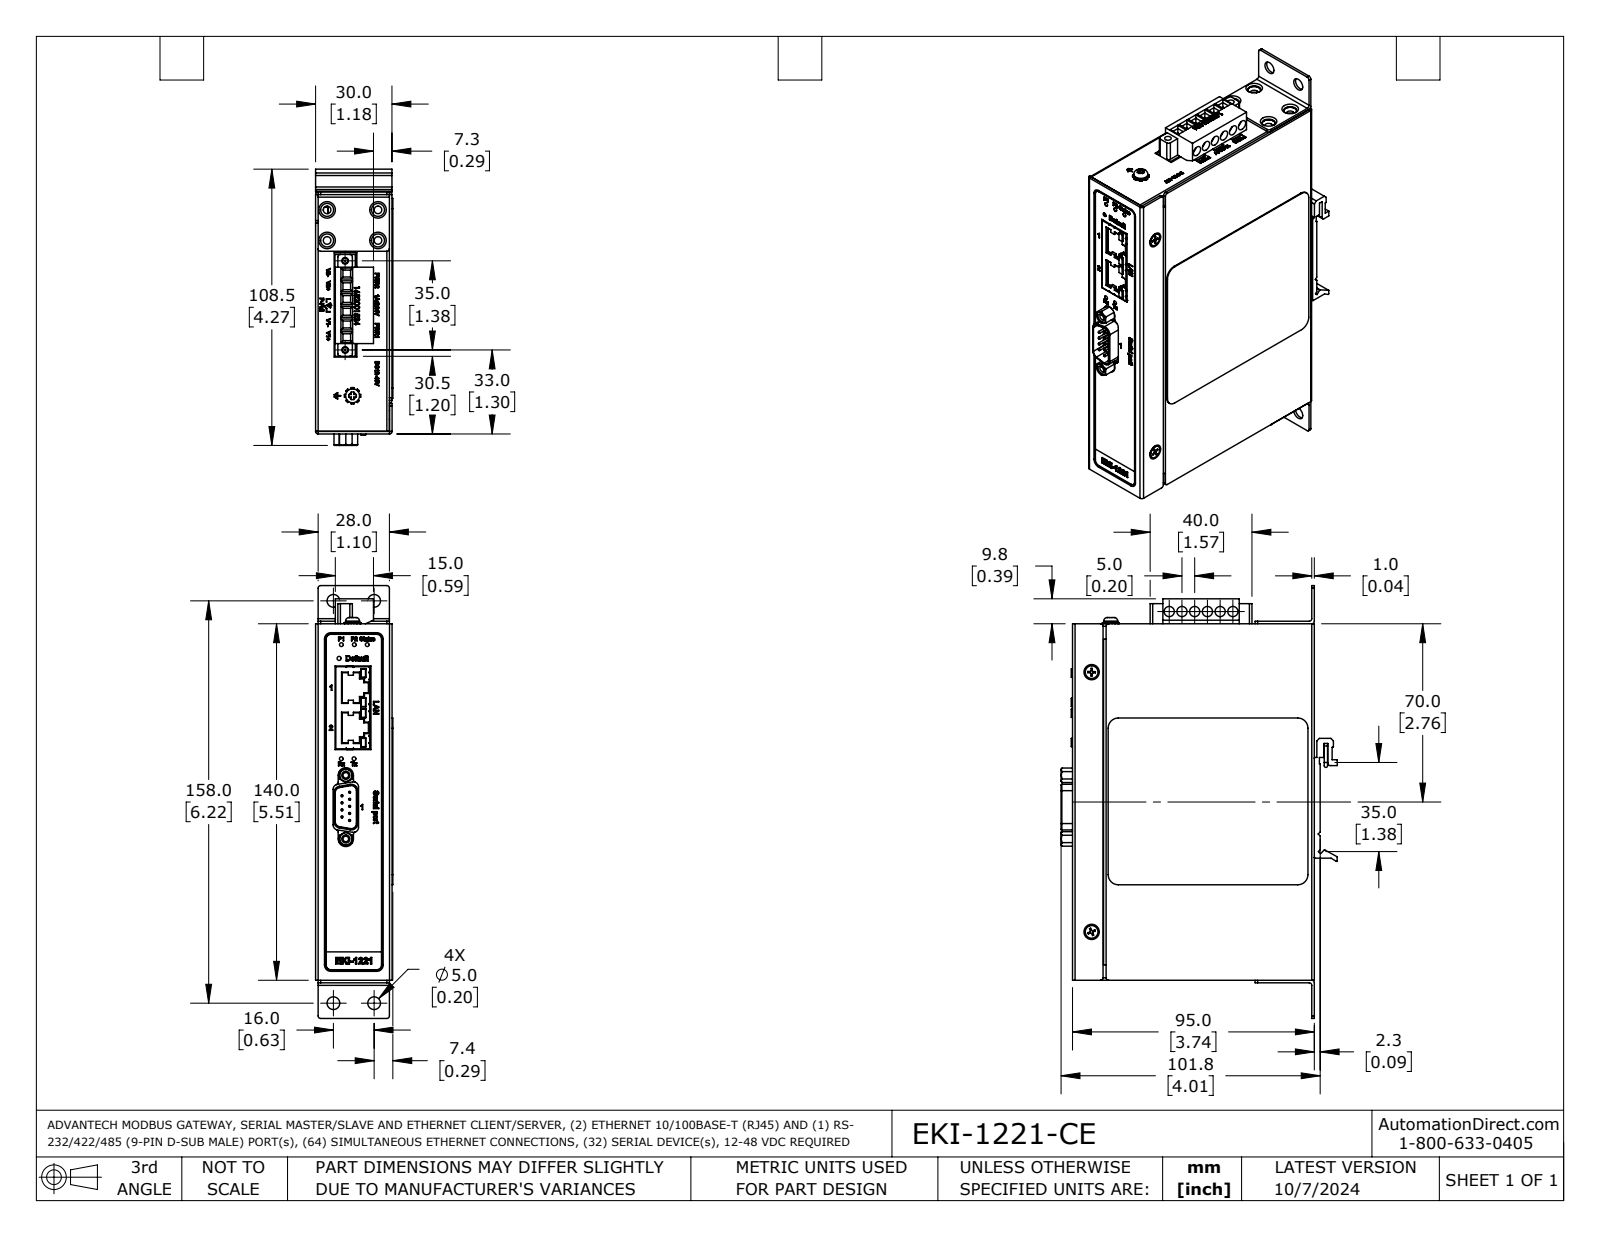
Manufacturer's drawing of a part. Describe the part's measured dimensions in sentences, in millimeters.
The part is named "EKI-1221-CE fxt". Its 3-D file was written by "SolidWorks 2021 (AUTOMOTIVE_DESIGN)". It is 14 solids with 2130 faces: 1281 planar, 376 cylindrical and 473 other. Overall it measures 170 by 108.5 by 30.4 millimeters. Its volume is 366 900 cubic millimeters and its surface area 110 100 square millimeters. Round holes: 15 of diameter 3.5, 11 of diameter 1.5, 9 of diameter 3, 6 of diameter 4, 4 of diameter 5, 4 of diameter 5.1, 2 of diameter 2.1, 2 of diameter 2.2, 2 of diameter 2.6, 1 of diameter 1.6, 1 of diameter 2.5. Round bosses or shafts: 9 of diameter 5, 9 of diameter 0.8, 6 of diameter 1.3, 2 of diameter 2.8, 1 of diameter 5.5, 1 of diameter 3. Partial cylindrical surfaces (rounded edges, fillets, slot ends): 45 of radius 1, 28 of radius 0.4, 12 of radius 2, 10 of radius 2.5, 6 of radius 0.3, 6 of radius 2.8, 5 of radius 0.5, 4 of radius 1.9. The main face-to-face distances are 1, 29, 30, 0.4, 1, 30.4, 1.3, 27.9, 28, 94.5. The hole center spacings are 5, 10, 15, 20, 25, 38, 6.7, 7.2.
